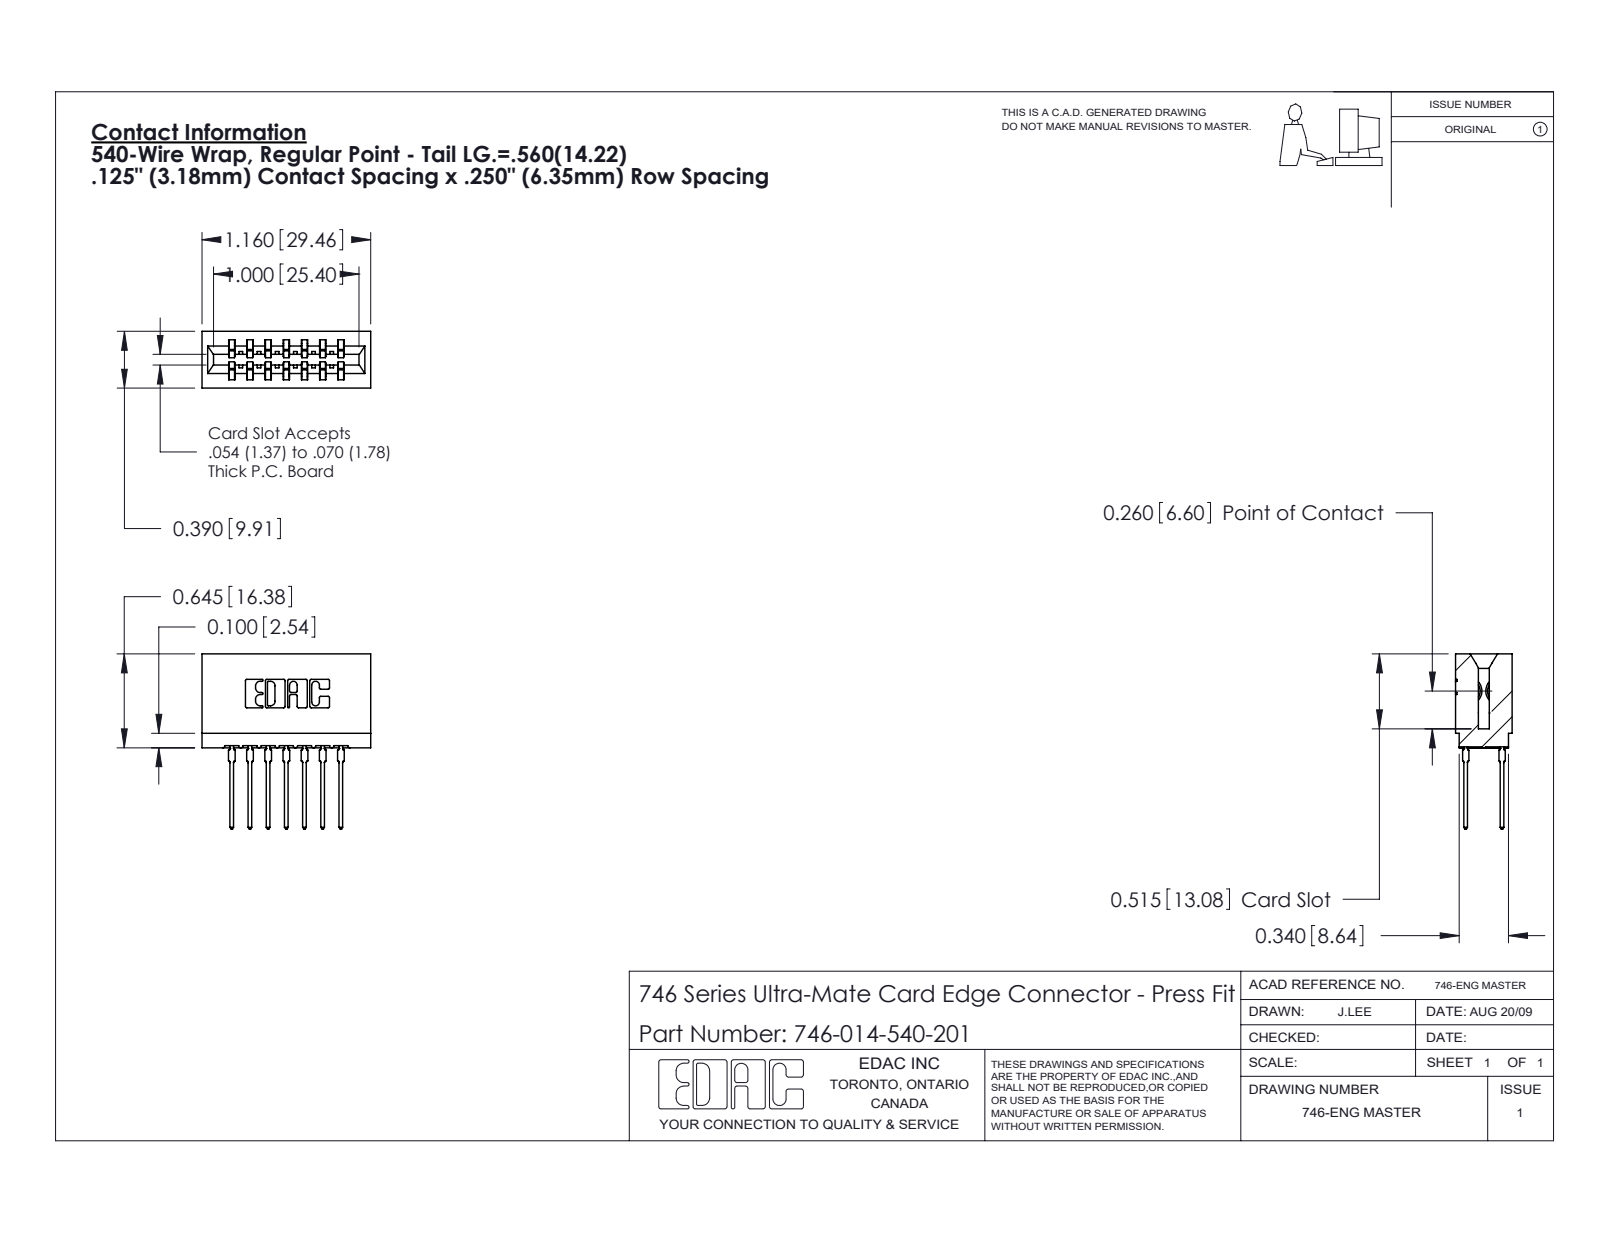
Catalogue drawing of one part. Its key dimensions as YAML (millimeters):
part_name: "746-292-001_540; 746 Part_.515 Slot Depth - 01; 746-014-540-201"
step_written_by: "SolidWorks 2020 (CONFIG_CONTROL_DESIGN)"
units: millimeters
bodies: {solids: 15, faces: 1350, planar: 699, cylindrical: 287, other: 364}
overall_size: [30.6, 29.5, 9.9]
volume: 3420
surface_area: 4995
partial_cylinders:
  - {radius: 0.5, count: 28}
  - {radius: 0.3, count: 22}
  - {radius: 0.1, count: 8}
  - {radius: 0.3, count: 8}
  - {radius: 0.4, count: 8}
  - {radius: 0.2, count: 6}
  - {radius: 0.8, count: 6}
  - {radius: 0.7, count: 3}
face_to_face_distances: [6.4, 8.5, 1.4, 1.1, 3.2, 12.7, 3.2, 2.1, 7.4, 5.3]
